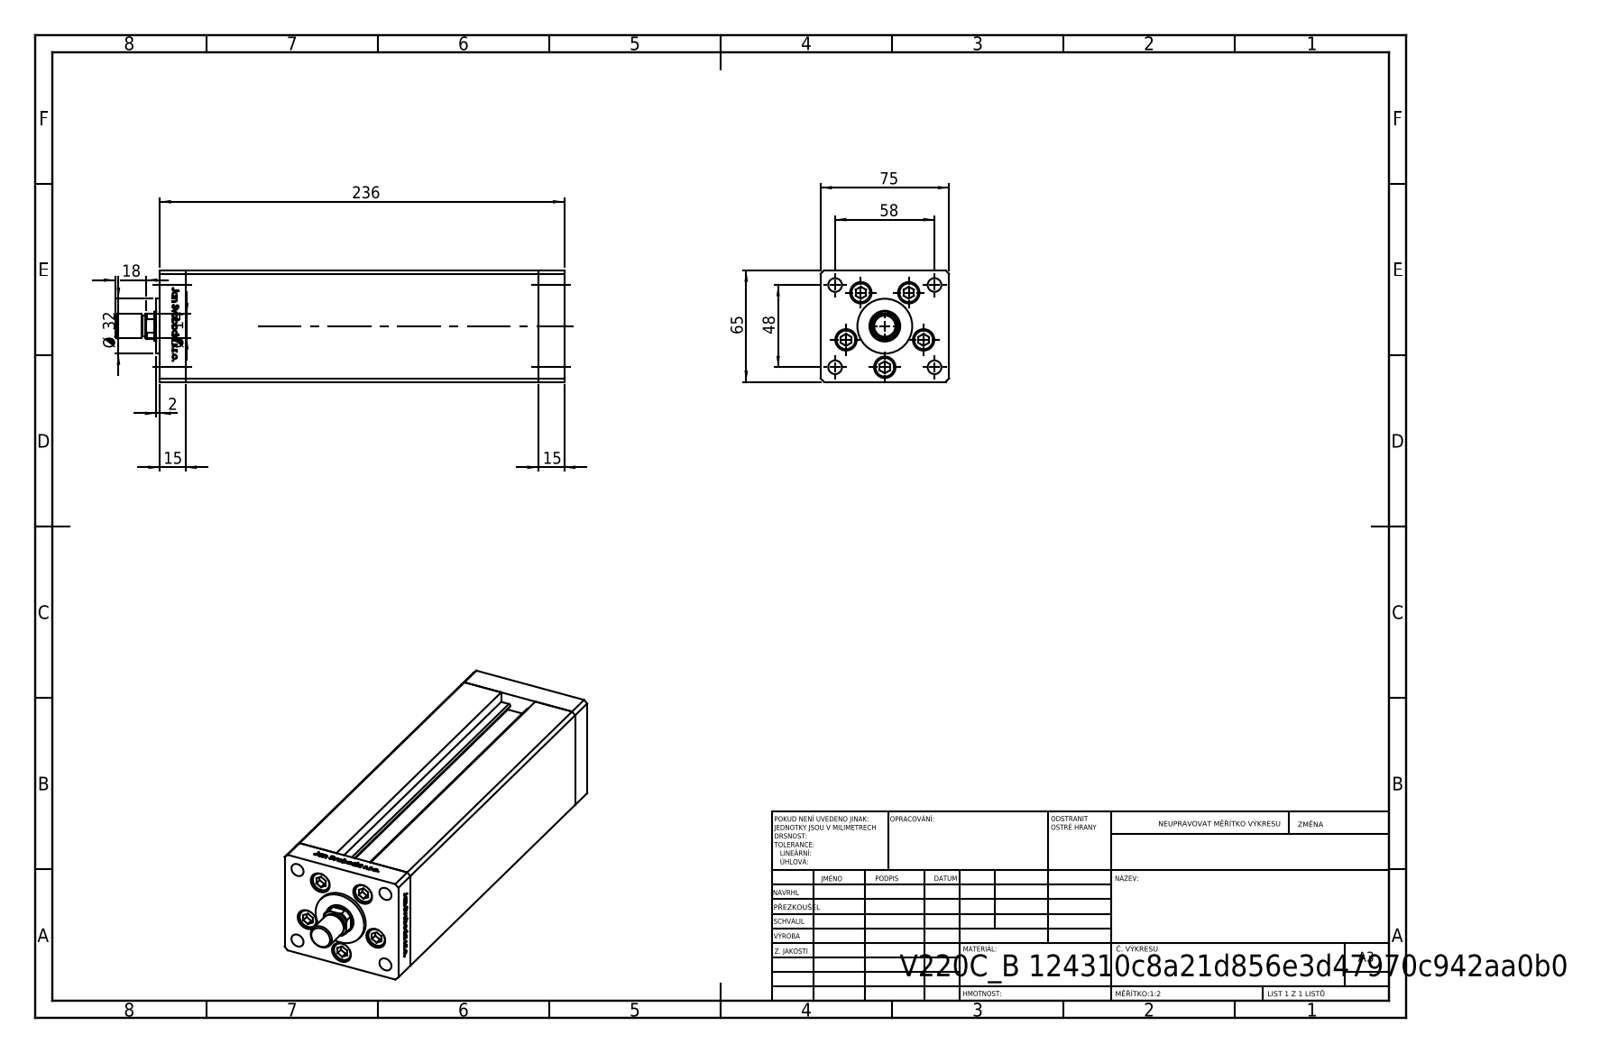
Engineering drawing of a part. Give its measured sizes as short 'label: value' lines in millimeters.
name: V220C BACK_B; V220C_FRONT_B; V220C_B MIDDLE; ALLEN BOLT (+2 more)
written by: SolidWorks 2019 (CONFIG_CONTROL_DESIGN)
unit: mm
bodies: 15 solids, 1188 faces (463 planar, 147 cylindrical, 578 other)
size: 262 × 75 × 65
volume: 1 013 000 mm³; area: 158 642 mm²
holes: 5× ⌀9, 5× ⌀12.5, 4× ⌀8, 2× ⌀2, 2× ⌀13.16, 1× ⌀10, 1× ⌀18
bosses: 5× ⌀8, 1× ⌀32, 1× ⌀14, 1× ⌀12
rounds: 2× R0.93, 1× R8.5
face distances: 75, 65, 15, 206, 221, 236, 10.5, 54.5, 26.25, 48.75
hole spacings: 24, 37.64, 15.67, 17.22, 27.71, 28.83, 29, 32.63
